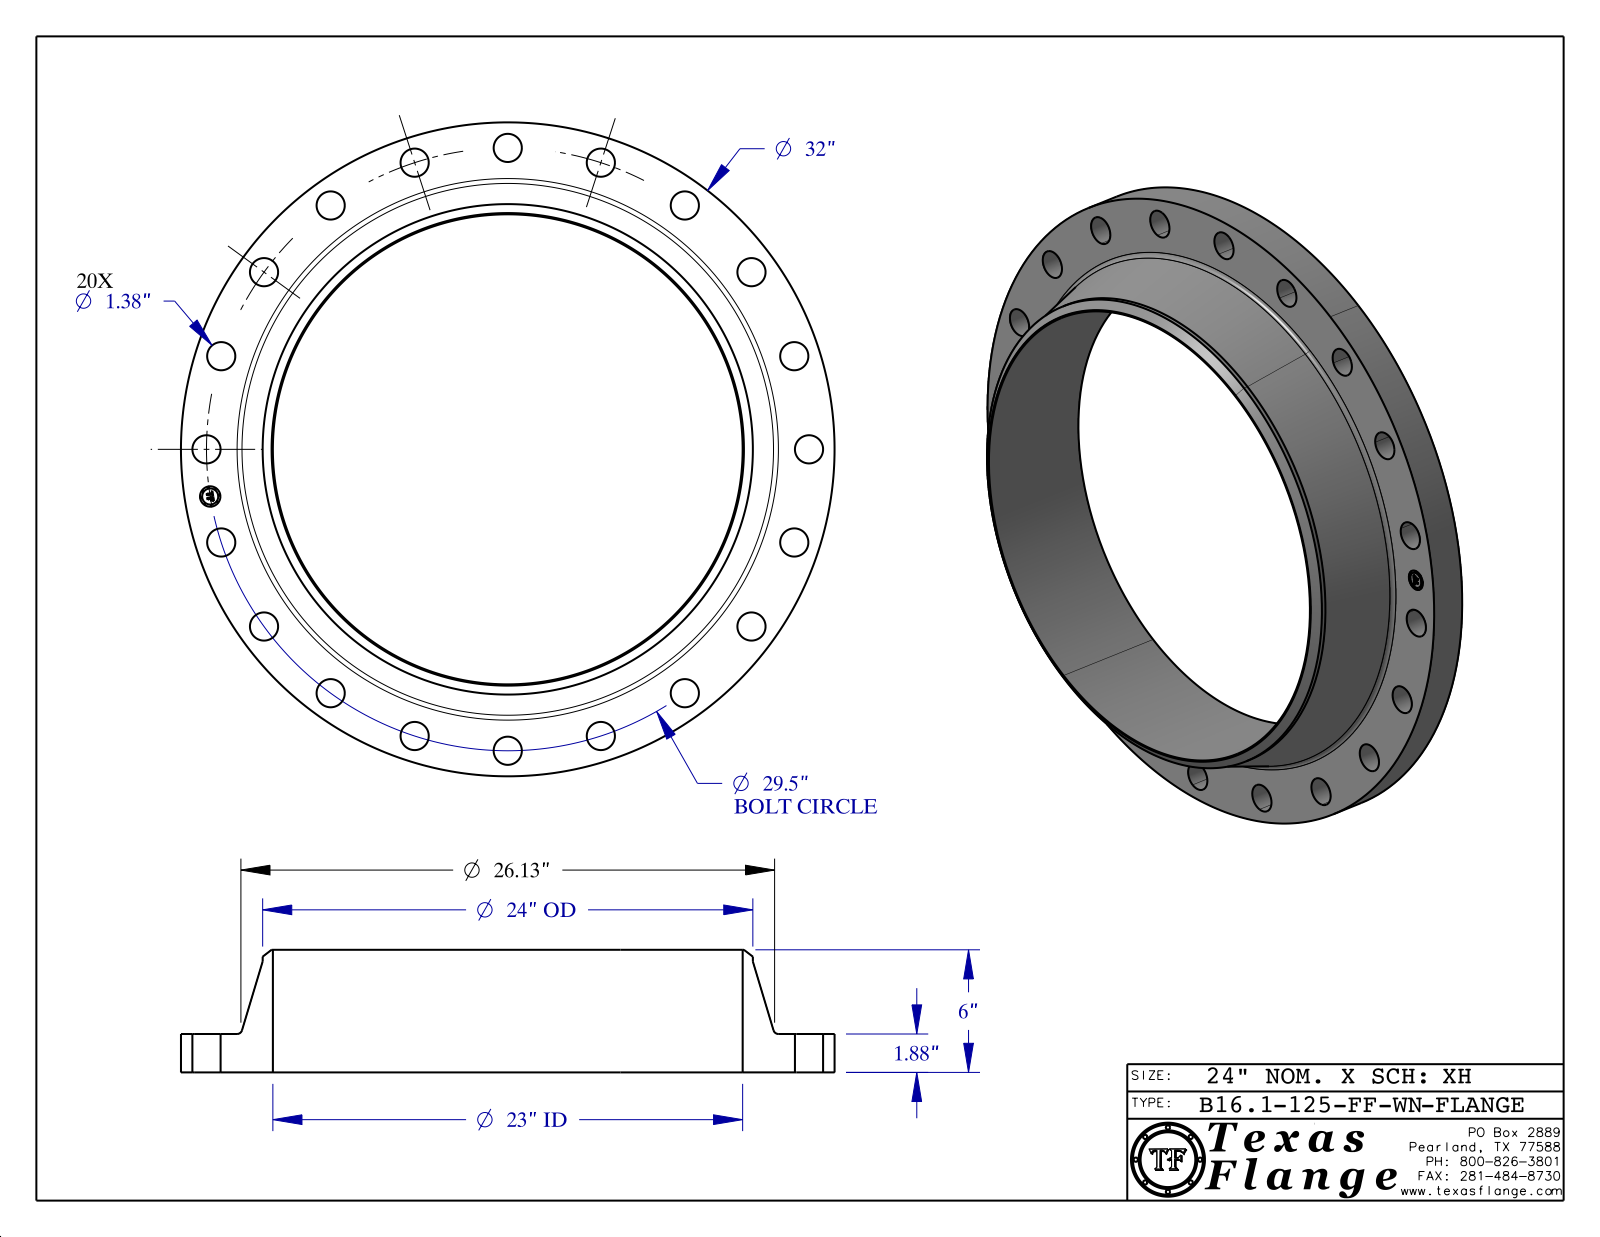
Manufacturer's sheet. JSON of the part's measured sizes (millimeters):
{"part_name": "B16.1, Class 125-FF-WN", "step_written_by": "CATIA V5 STEP AP214 (AUTOMOTIVE_DESIGN)", "units": "millimeters", "bodies": {"solids": 1, "faces": 440, "planar": 368, "cylindrical": 66, "other": 6}, "overall_size": [812.8, 812.8, 152.4], "volume_mm3": 15870000, "surface_area_mm2": 1118000, "round_holes": [[35.1, 20], [25.4, 1], [584.2, 1]], "round_bosses_or_shafts": [[1.5, 8], [812.8, 1], [609.6, 1], [20, 1]], "face_to_face_distances": [47.8, 152.4, 104.6, 47.4, 0.4, 105, 7.6, 7.4, 1.4, 4.9], "hole_center_spacings": [374.7, 740.1, 117.2, 440.4, 529.8, 606.2, 667.6, 231.5]}
